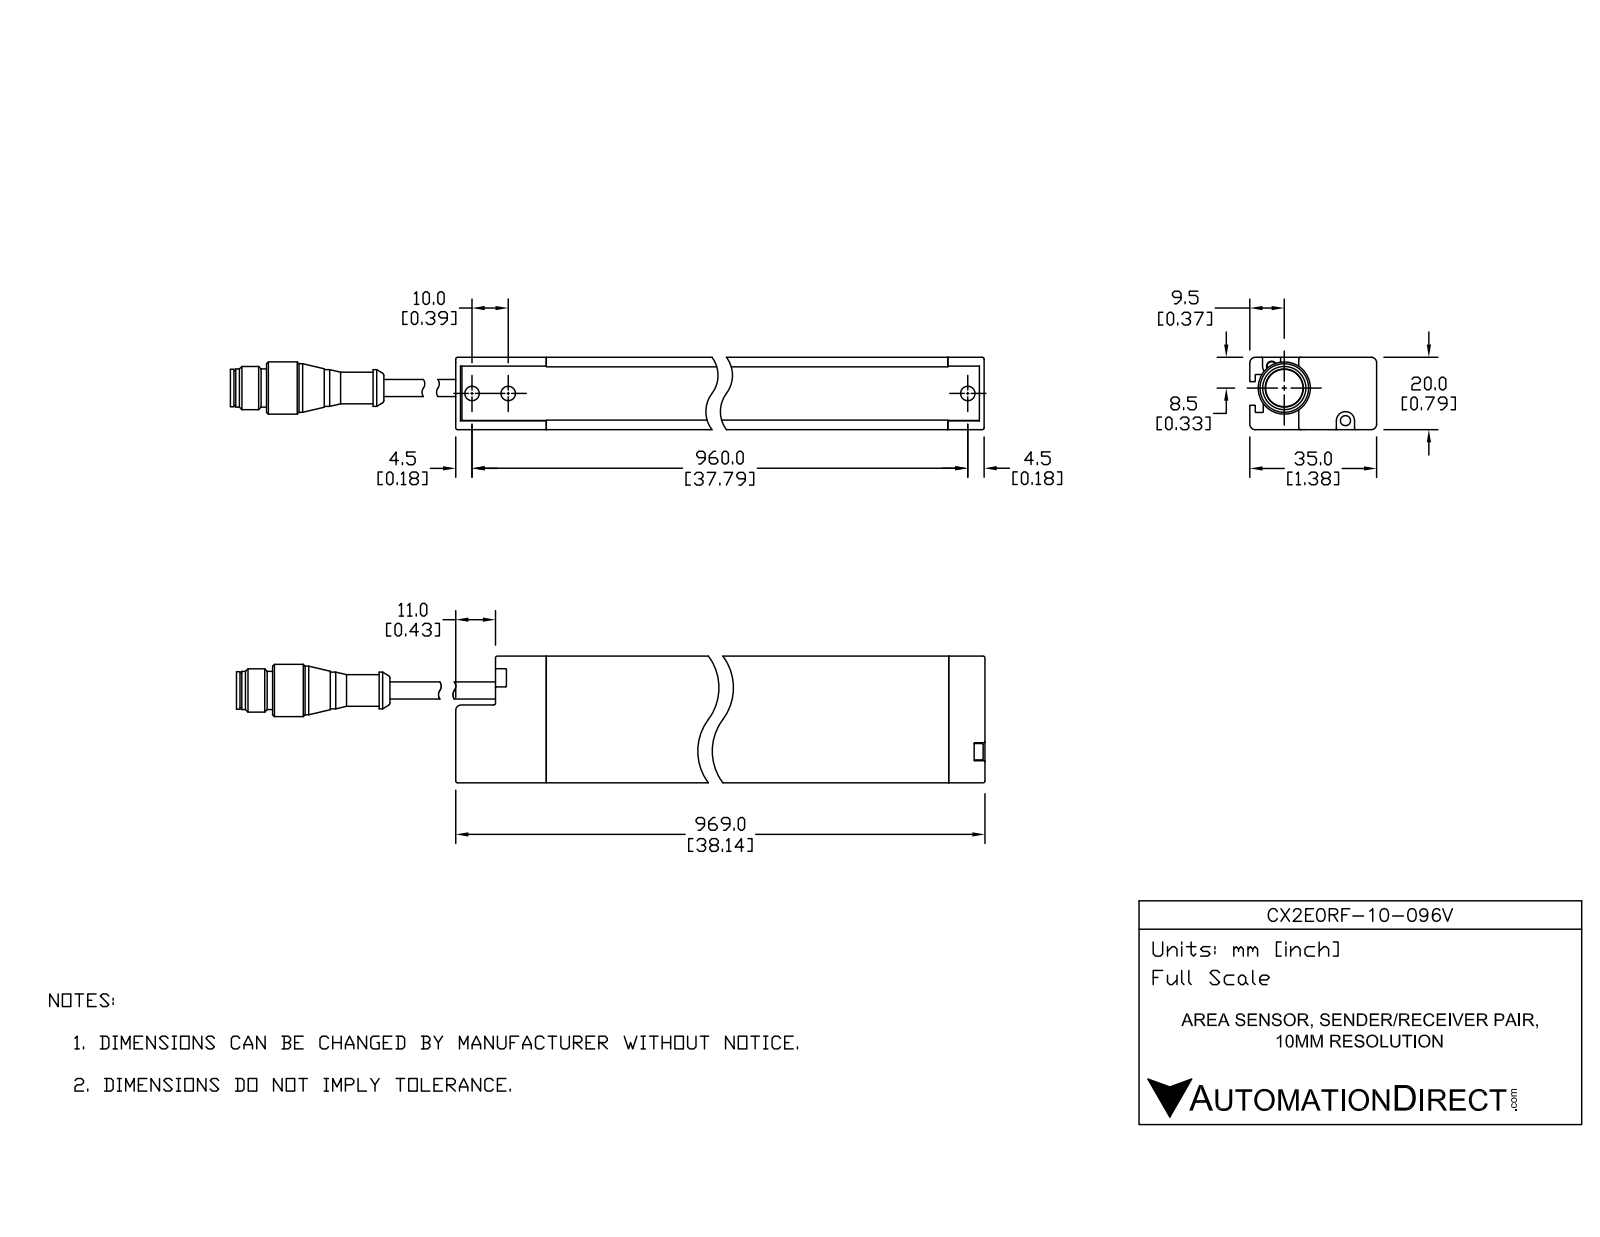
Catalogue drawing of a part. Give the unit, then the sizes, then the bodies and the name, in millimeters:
Units: millimetres
Overall size (bounding box): 1046.84 × 507.67 × 156.28
Round holes (diameter × count): ⌀2.8 ×8, ⌀6.5 ×2, ⌀8 ×2
Round bosses / shafts (diameter × count): ⌀2.01 ×8, ⌀14.42 ×2, ⌀13.42 ×2, ⌀11.93 ×2, ⌀10.53 ×2, ⌀10.33 ×2, ⌀10.13 ×2, ⌀9.53 ×2
Partial cylindrical surfaces — rounded edges, fillets, slot ends (radius × count): R0.2 ×96, R0.5 ×26, R1.5 ×10, R2.5 ×8, R0.3 ×4
Main face-to-face distances: 136.29, 20, 2, 156.29, 116.29, 439.34, 30.9, 469.37, 3.7, 34.6
Hole centre spacings: 15, 20.4, 25.32, 494.43, 6.95, 9.66, 17.93, 19.15
Volume: 1 340 000 mm³ · Surface area: 316 465 mm²
Bodies: 14 solids, 638 faces (206 planar, 262 cylindrical, 170 other)
STEP written by: Unknown (AUTOMOTIVE_DESIGN)
